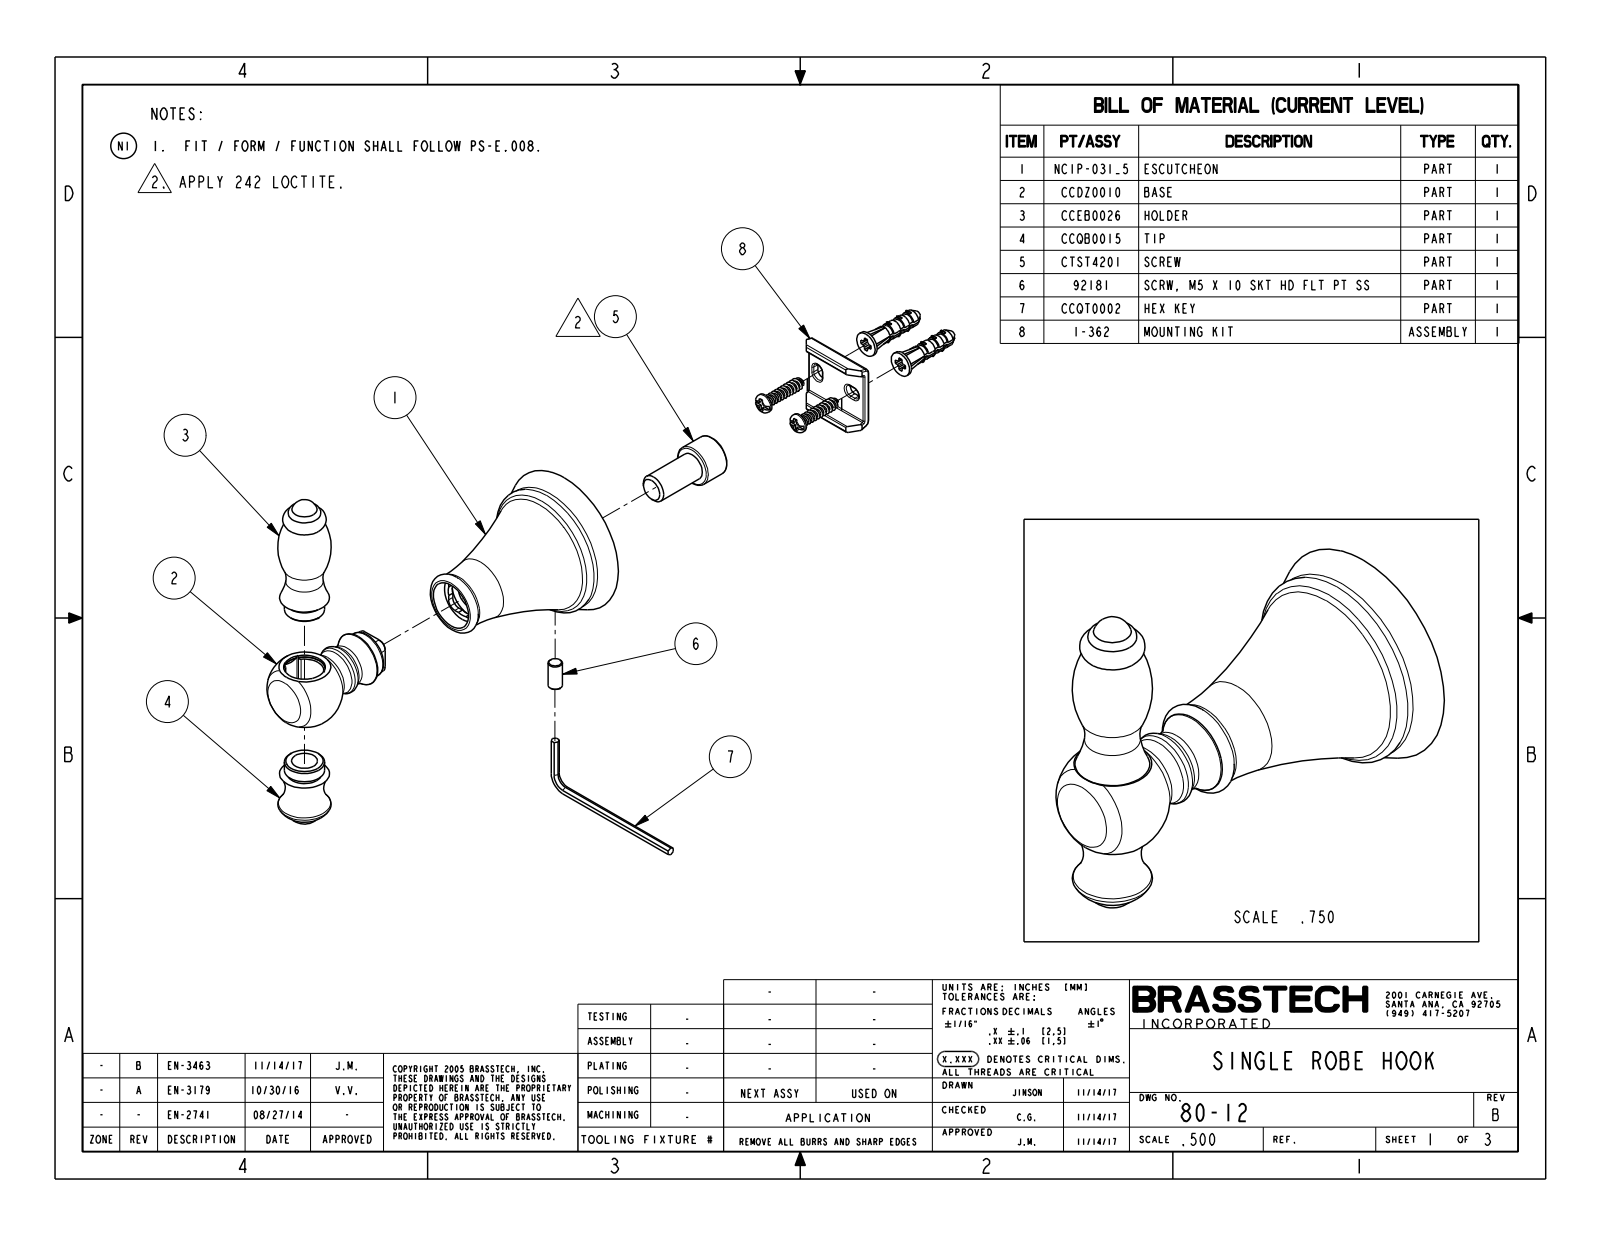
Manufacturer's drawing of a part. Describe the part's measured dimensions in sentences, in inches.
The part is named "NCIP-031_5; CCDZ0010; CCEB0026; CCQB0015 (+4 more)". Its 3-D file was written by "PRO/ENGINEER BY PARAMETRIC TECHNOLOGY CORPORATION, 2013150 (CONFIG_CONTROL_DESIGN)". It is 7 solids with 307 faces: 95 planar, 102 cylindrical and 110 other. Overall it measures 3.72 by 3.169 by 2.1 inches. Its volume is 2.477 cubic inches and its surface area 42.89 square inches. Round holes: 1 of diameter 0.165, 1 of diameter 0.236, 1 of diameter 0.339, 1 of diameter 0.354, 1 of diameter 0.394, 1 of diameter 0.417, 1 of diameter 0.571, 1 of diameter 0.669, 1 of diameter 0.685, 1 of diameter 0.945, 1 of diameter 1.68, 1 of diameter 1.93. Round bosses or shafts: 1 of diameter 0.585, 1 of diameter 0.551, 1 of diameter 0.472, 1 of diameter 0.197. Partial cylindrical surfaces (rounded edges, fillets, slot ends): 22 of radius 0.02, 8 of radius 0.118, 6 of radius 0.079, 4 of radius 0.012, 4 of radius 0.039, 4 of radius 0.089, 1 of radius 0.264, 1 of radius 0.272. The main face-to-face distances are 0.098, 0.7, 0.602, 0.217, 0.09, 0.61, 0.531, 0.079, 1.669, 1.235. The hole center spacings are 3.07.
